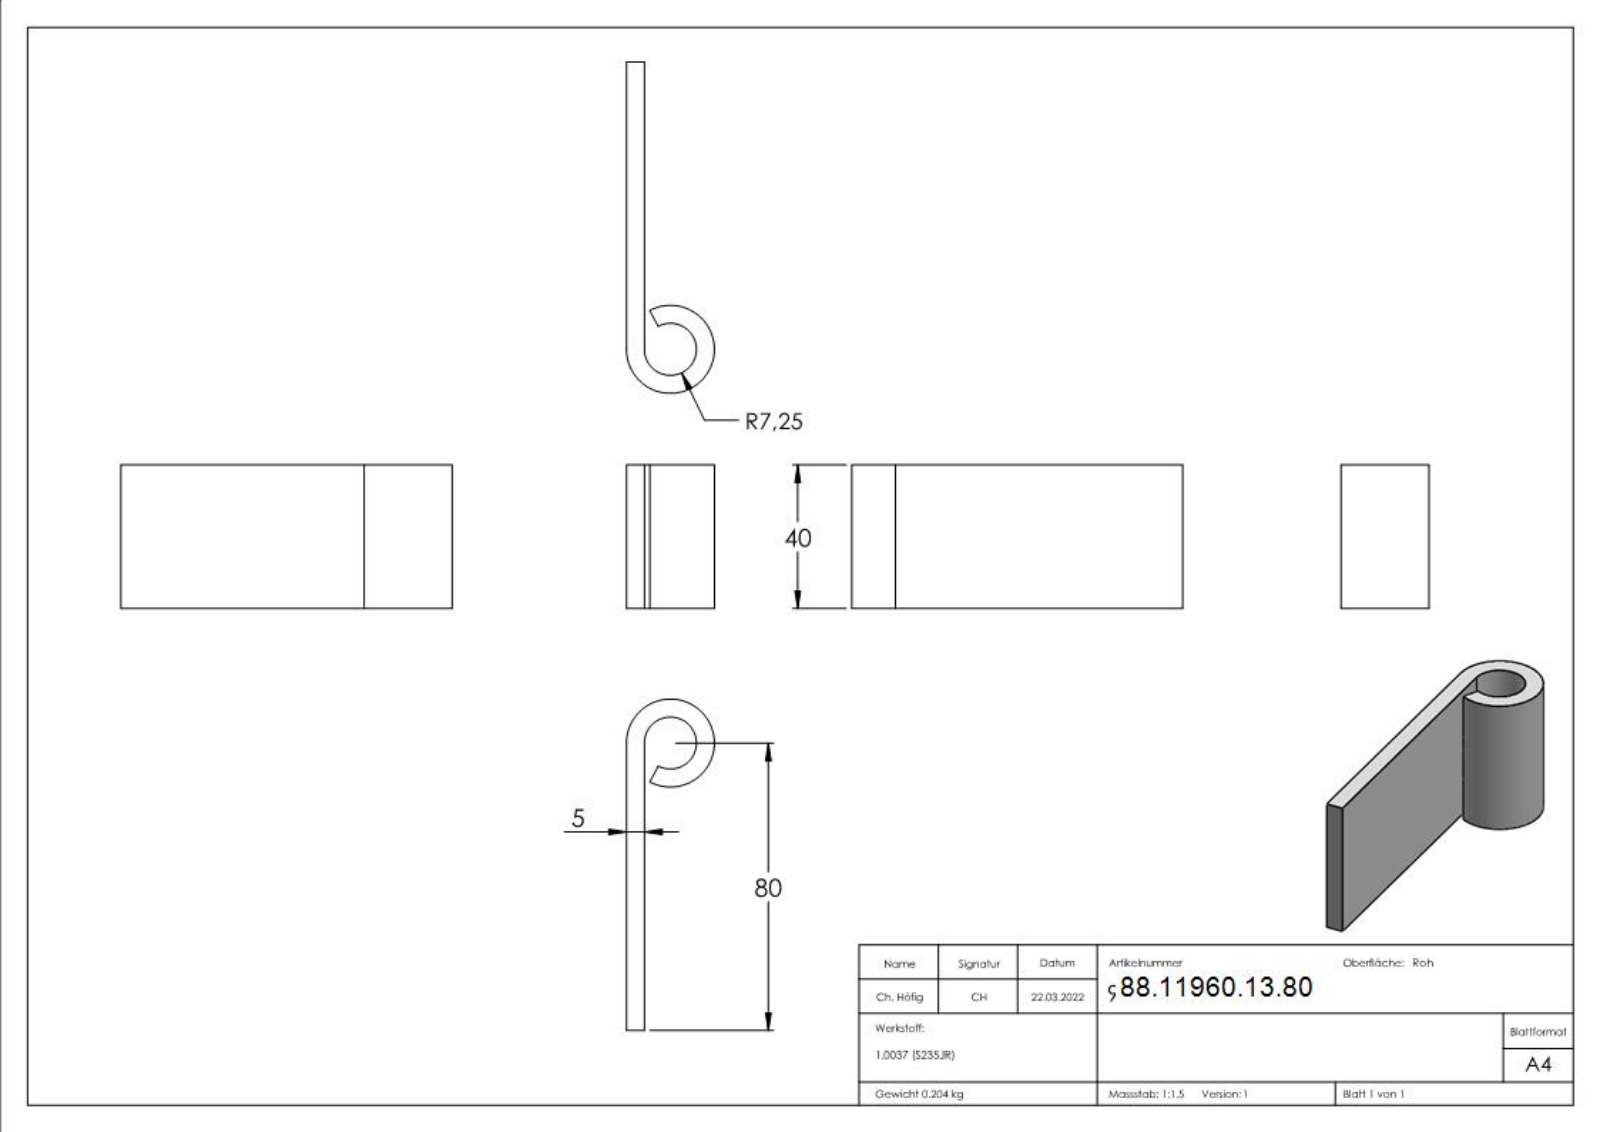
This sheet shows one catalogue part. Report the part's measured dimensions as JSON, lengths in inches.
{"part_name": "960-13-80", "step_written_by": "SolidWorks 2018 (CONFIG_CONTROL_DESIGN)", "units": "inches", "bodies": {"solids": 1, "faces": 226, "planar": 109, "cylindrical": 2, "other": 115}, "overall_size": [3.632, 1.575, 0.965], "volume_in3": 1.595, "surface_area_in2": 18.87, "round_holes": [[0.571, 1]], "round_bosses_or_shafts": [[0.965, 1]], "face_to_face_distances": [0.197, 1.575, 0.117, 0.049, 0.065, 0.015, 0.226, 0.08, 0.054, 0.129]}
